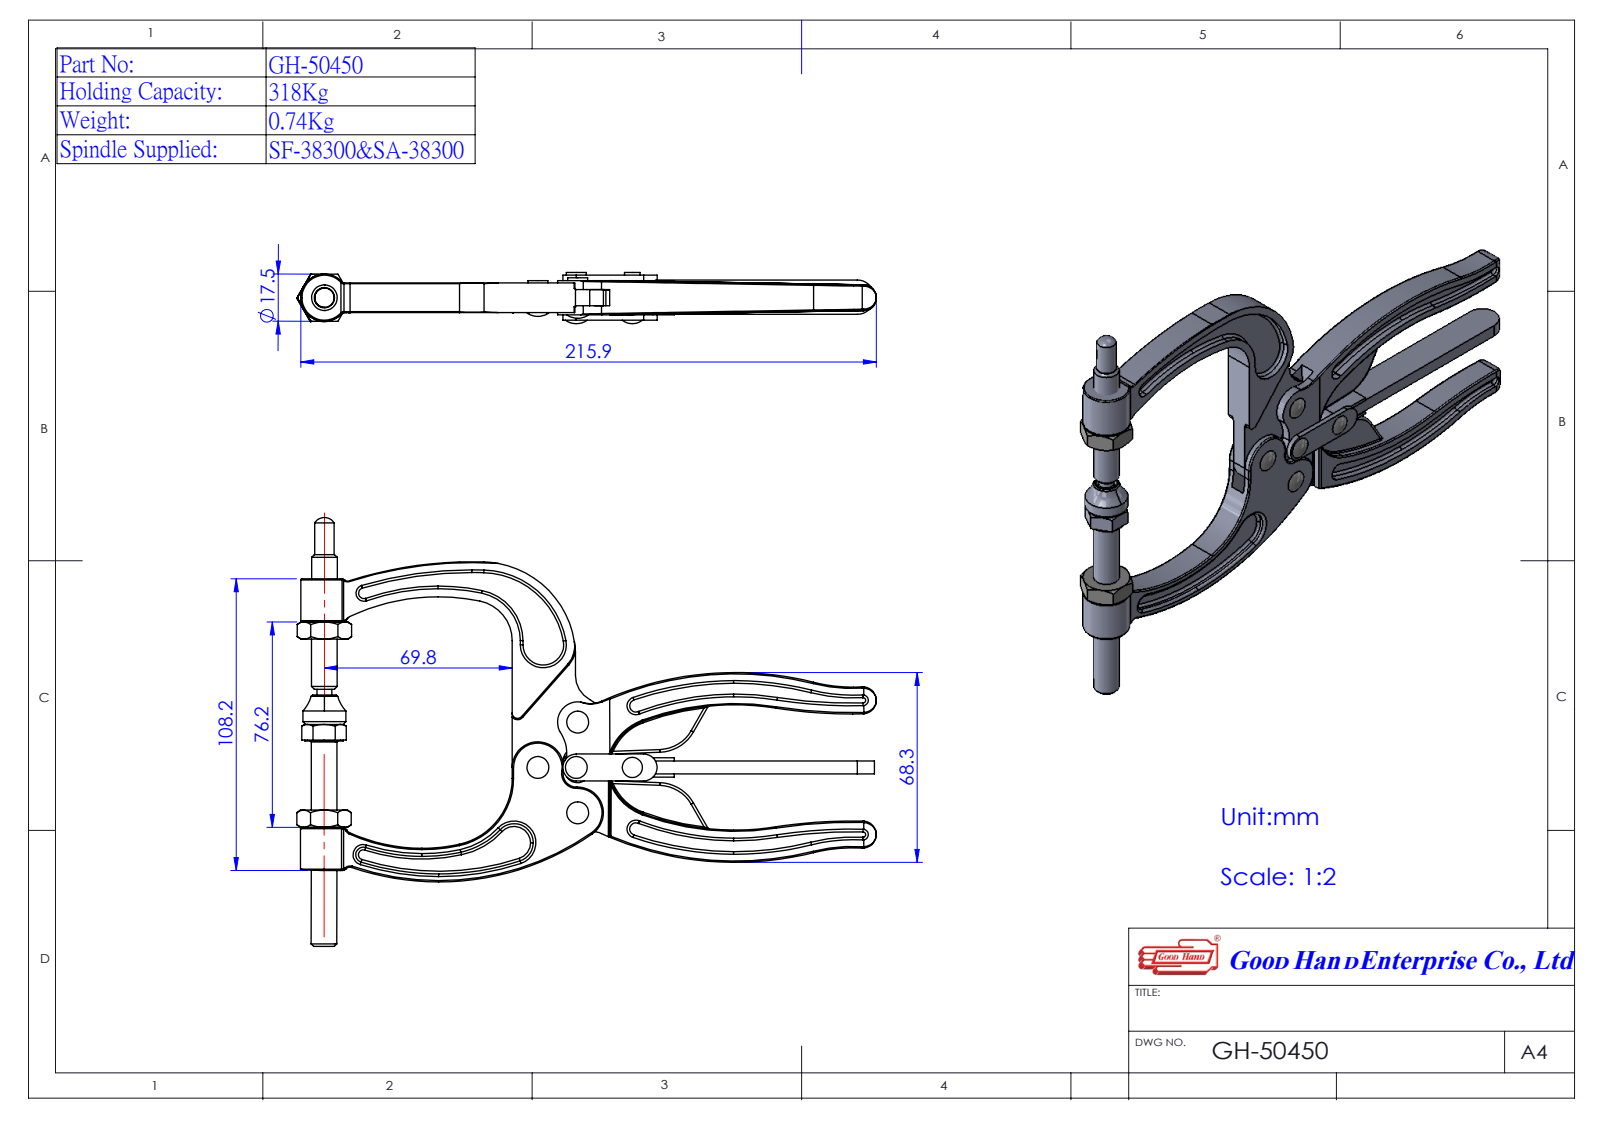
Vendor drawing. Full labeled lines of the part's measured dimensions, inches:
Part name (STEP PRODUCT): 35045002-1^493802(GH-50450); 493802(GH-50450); Group2^493802(GH-50450); Group3^493802(GH-50450) (+2 more)
STEP written by: SolidWorks 2016 (AUTOMOTIVE_DESIGN)
Units: inches
Bodies: 8 solids, 389 faces (125 planar, 210 cylindrical, 54 other)
Overall size (bounding box): 8.418 × 6.29 × 0.748
Volume: 5.839 in³ · Surface area: 81.74 in²
Round holes (diameter × count): ⌀0.197 ×4
Round bosses / shafts (diameter × count): ⌀0.291 ×4, ⌀0.375 ×2, ⌀0.75 ×1, ⌀0.63 ×1, ⌀0.283 ×1, ⌀0.228 ×1, ⌀0.218 ×1
Partial cylindrical surfaces — rounded edges, fillets, slot ends (radius × count): R0.079 ×13, R0.197 ×6, R0.039 ×4, R0.394 ×4, R0.591 ×4, R0.13 ×2, R0.187 ×2, R0.295 ×2
Main face-to-face distances: 0.122, 0.311, 0.189, 0.132, 0.368, 0.236, 0.213, 0.024, 0.018, 0.207
Hole centre spacings: 0.662, 0.882, 0.562, 1.324
